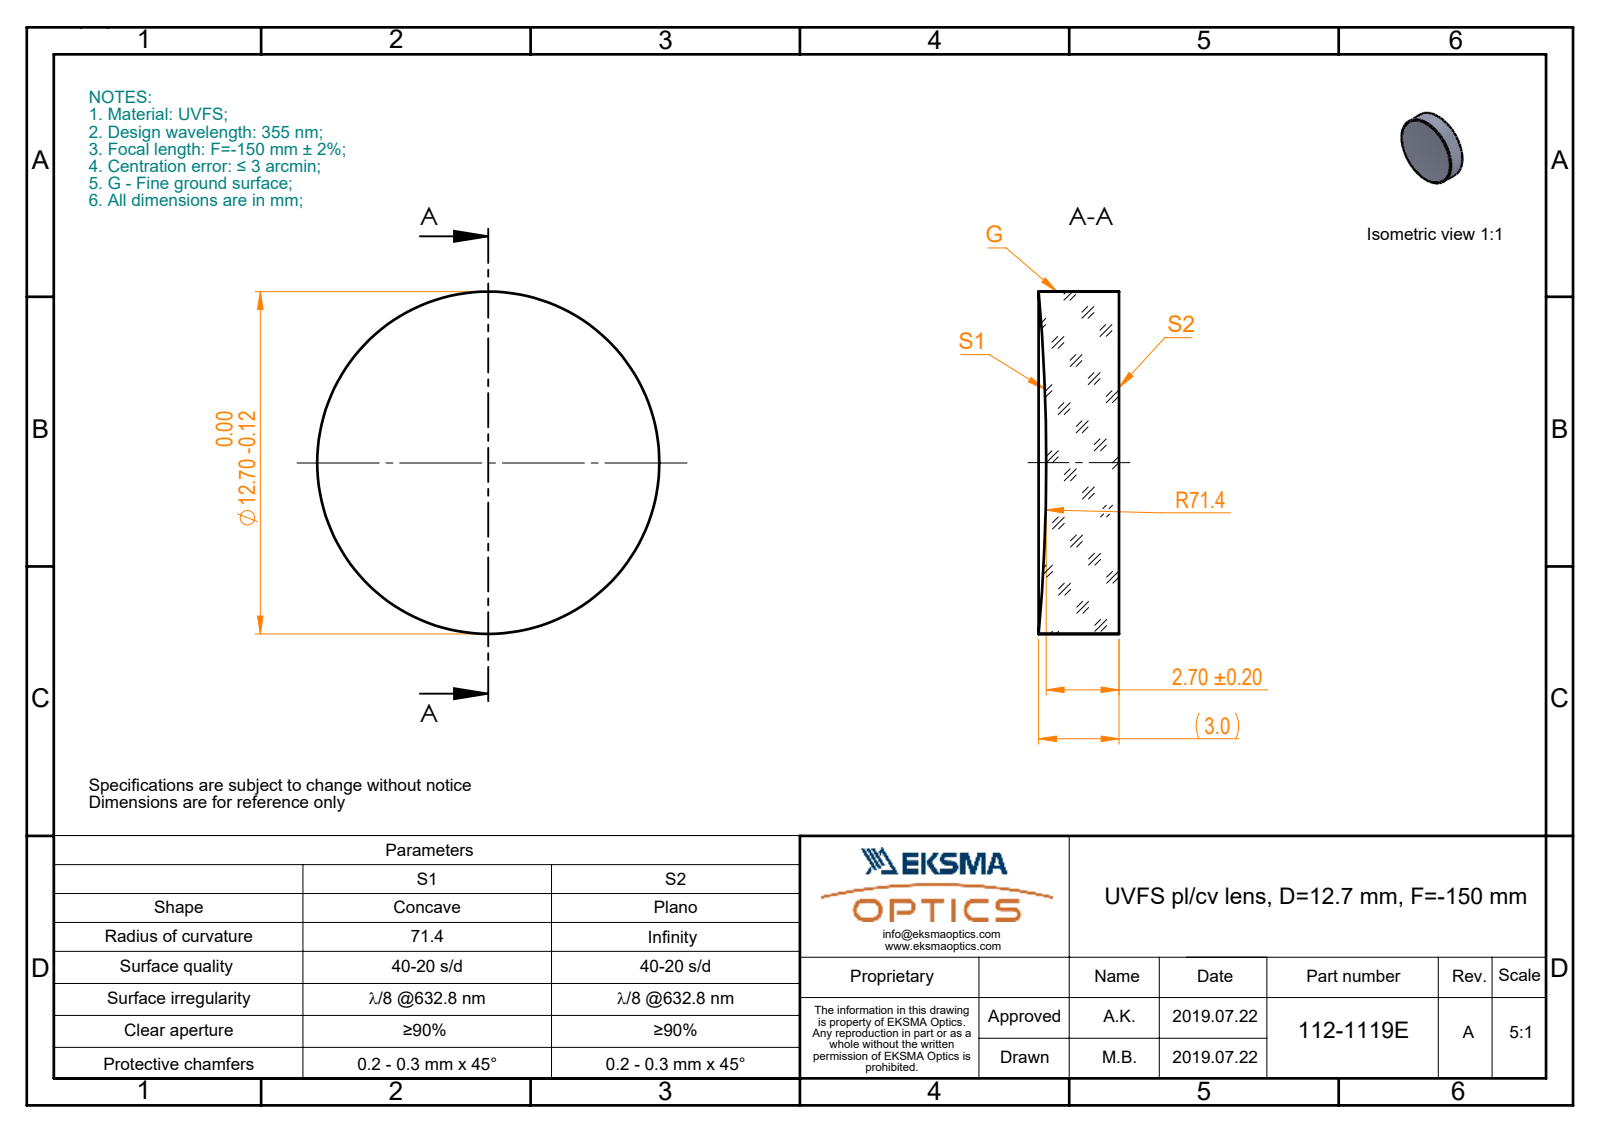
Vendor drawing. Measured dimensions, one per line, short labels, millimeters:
name: 112-1119E UVFS pl-cv 12.7 F-150
written by: SolidWorks 2017 (CONFIG_CONTROL_DESIGN)
unit: mm
bodies: 1 solid, 5 faces (1 planar, 2 cylindrical, 2 other)
size: 12.7 × 12.7 × 2.98
volume: 360 mm³; area: 373 mm²
bosses: 1× ⌀12.7
